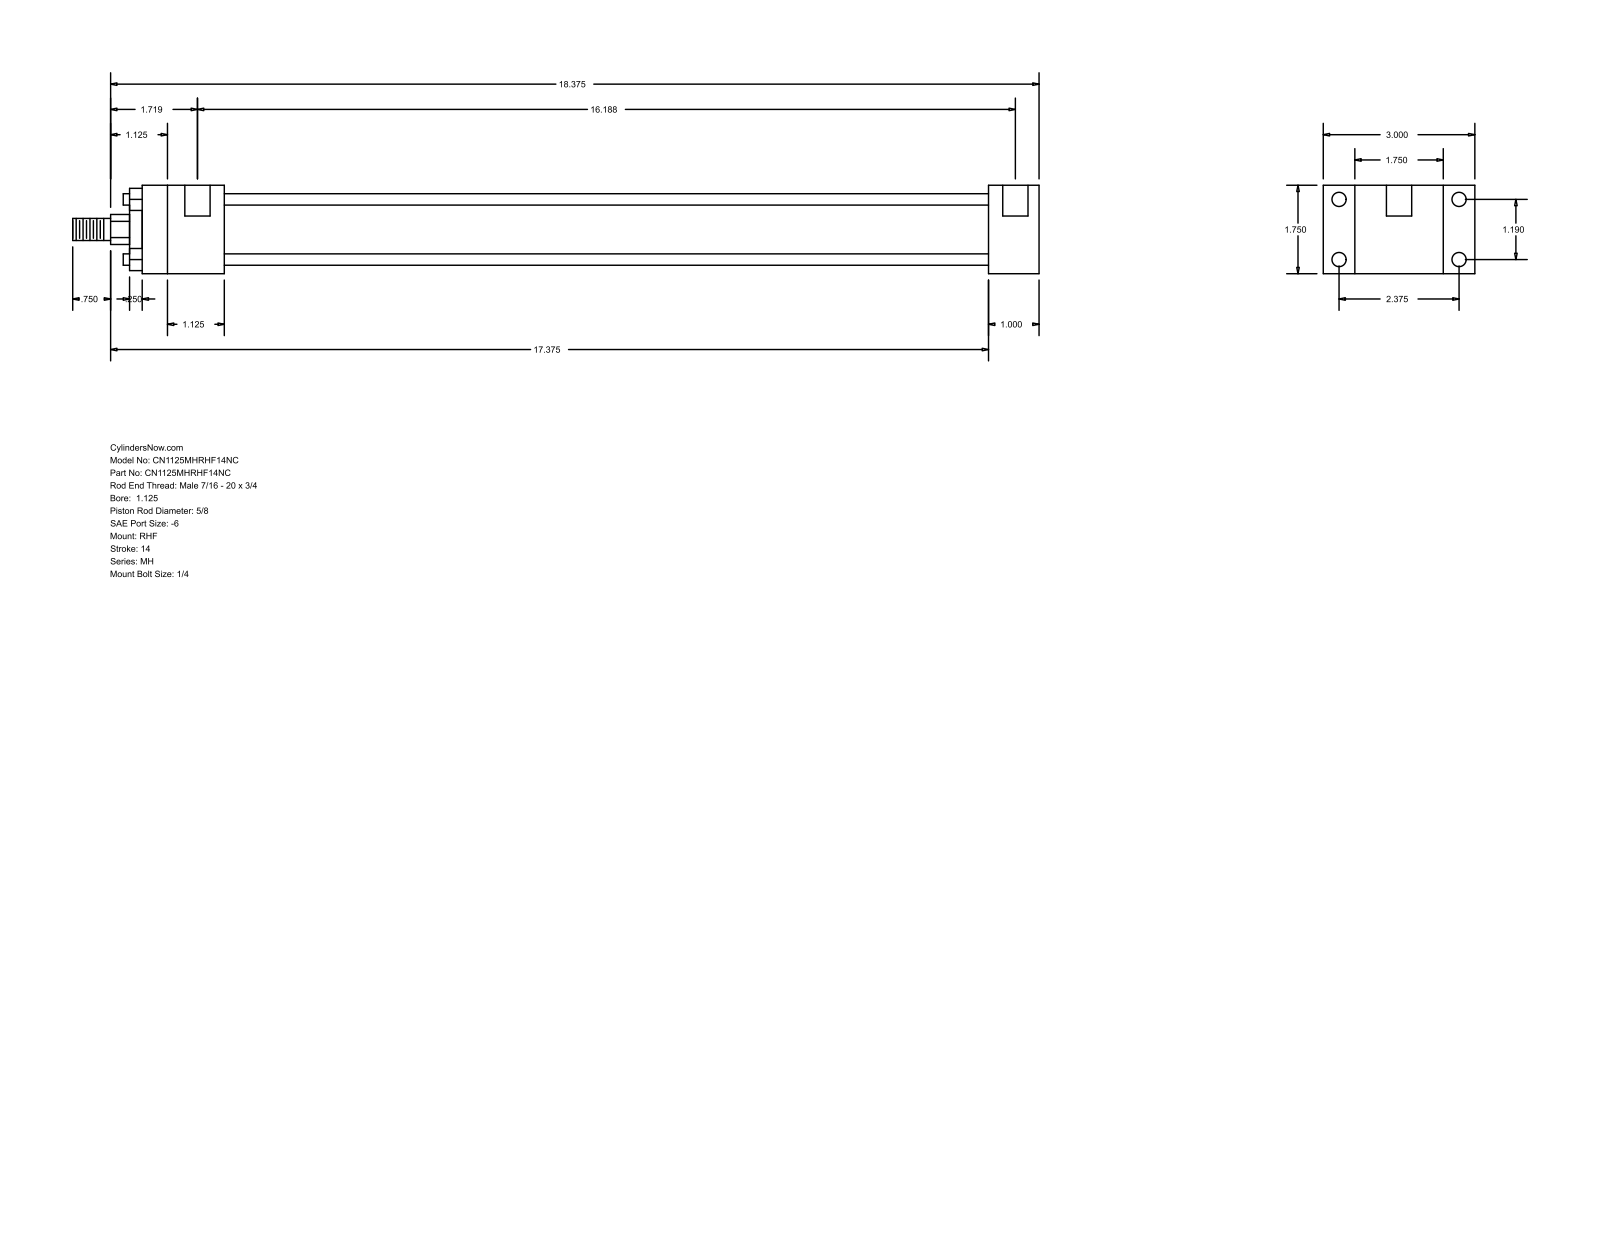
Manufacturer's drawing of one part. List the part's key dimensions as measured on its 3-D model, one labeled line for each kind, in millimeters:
Part name (STEP PRODUCT): MH_RHF__0112_0.625
STEP written by: GSSL Pune (CONFIG_CONTROL_DESIGN)
Units: millimetres
Bodies: 0 solids, 88 faces (60 planar, 28 cylindrical, 0 other)
Overall size (bounding box): 485.77 × 76.2 × 44.45
Round holes (diameter × count): ⌀5.56 ×4, ⌀7.14 ×4, ⌀12.7 ×2
Round bosses / shafts (diameter × count): ⌀5.71 ×4, ⌀34.92 ×1, ⌀28.57 ×1, ⌀15.88 ×1, ⌀11.11 ×1
Partial cylindrical surfaces — rounded edges, fillets, slot ends (radius × count): R7.54 ×1
Main face-to-face distances: 44.46, 15.87, 60.33, 25.41, 76.2, 384.17, 409.58, 41.27, 425.44, 450.85
Hole centre spacings: 30.22, 60.32, 67.47, 407.99, 3.17, 411.16
